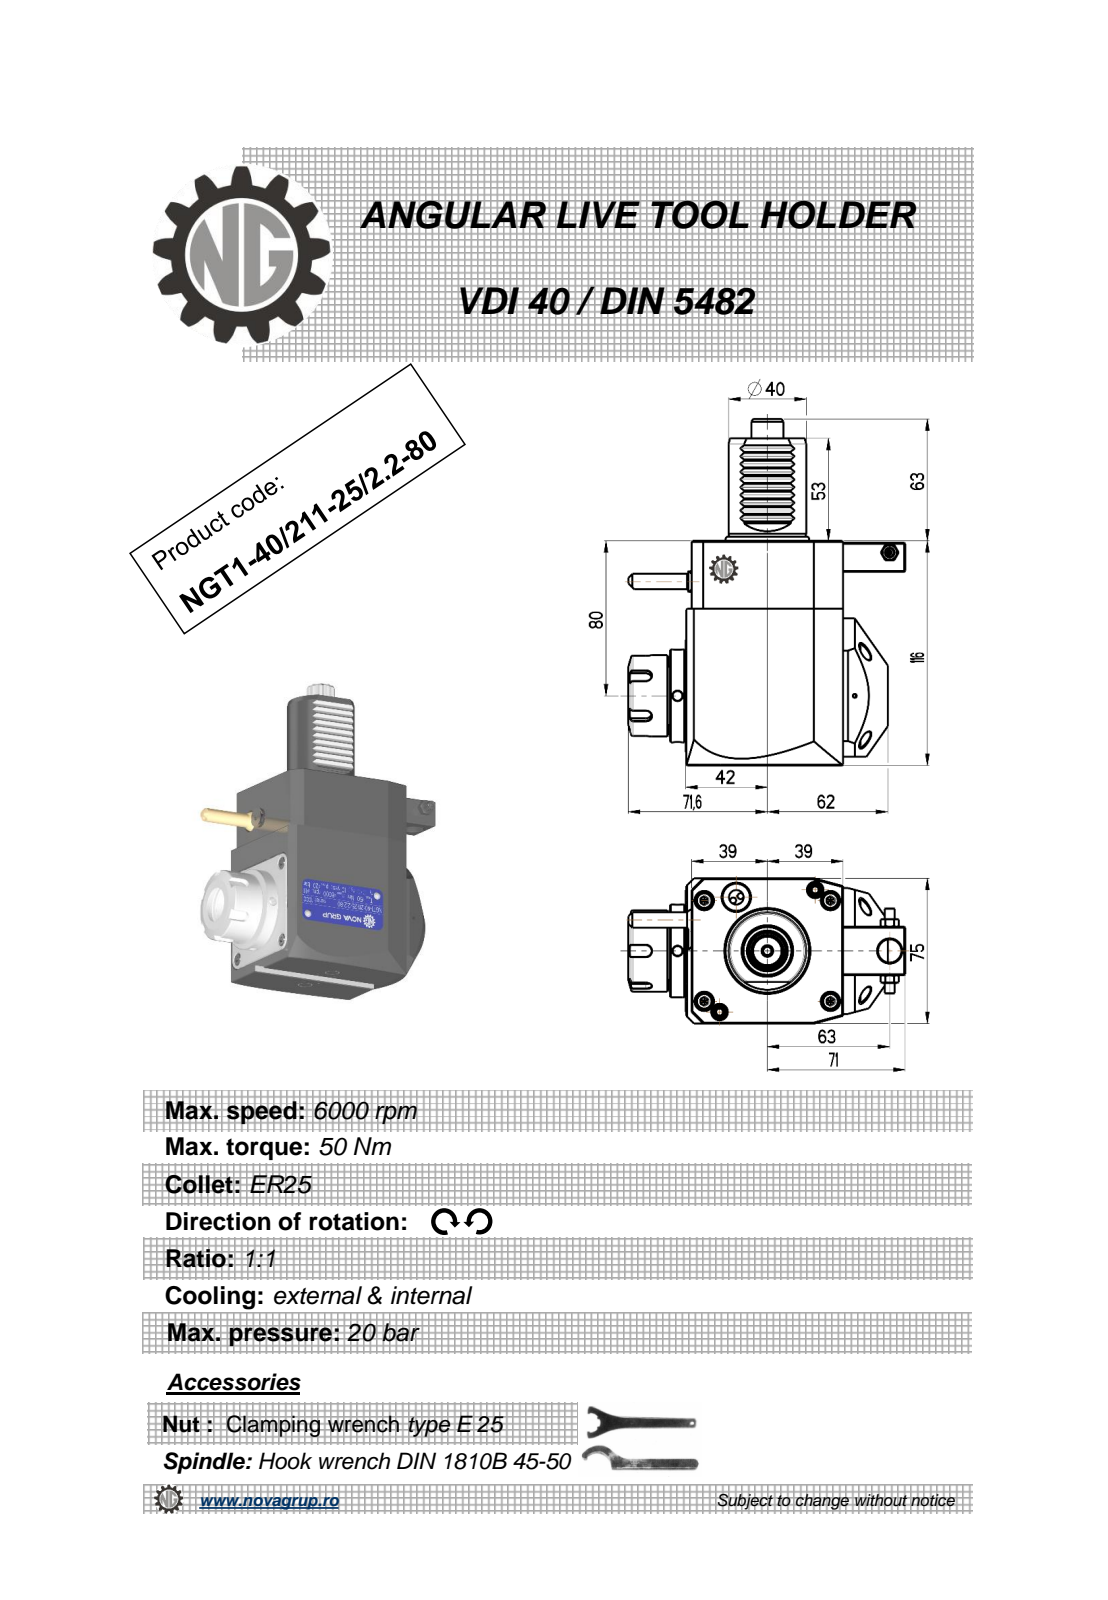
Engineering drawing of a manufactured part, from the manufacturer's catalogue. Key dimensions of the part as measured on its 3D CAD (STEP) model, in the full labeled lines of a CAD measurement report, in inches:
Part name (STEP PRODUCT): NGT1_40_211_25_2_2_80
STEP written by: PRO/ENGINEER BY PARAMETRIC TECHNOLOGY CORPORATION, 2010280 (CONFIG_CONTROL_DESIGN)
Units: inches
Bodies: 1 solid, 474 faces (184 planar, 124 cylindrical, 166 other)
Overall size (bounding box): 7.047 × 5.614 × 3.016
Volume: 52.75 in³ · Surface area: 107.8 in²
Round holes (diameter × count): ⌀0.197 ×3, ⌀0.165 ×2, ⌀0.118 ×1, ⌀0.374 ×1, ⌀0.472 ×1, ⌀0.799 ×1
Round bosses / shafts (diameter × count): ⌀1.89 ×1, ⌀1.654 ×1, ⌀1.575 ×1, ⌀1.476 ×1, ⌀1.299 ×1, ⌀0.441 ×1, ⌀0.353 ×1, ⌀0.315 ×1
Partial cylindrical surfaces — rounded edges, fillets, slot ends (radius × count): R0.119 ×18, R0.01 ×12, R0.012 ×10, R0.009 ×6, R0.118 ×5, R0.02 ×1, R0.266 ×1, R0.324 ×1
Main face-to-face distances: 2.953, 4.567, 3.189, 0.118, 3.071, 0.11, 3.181, 4.409, 0.984, 0.295
Hole centre spacings: 0.824, 1.821, 2.407, 2.48, 2.854, 4.301, 5.195
